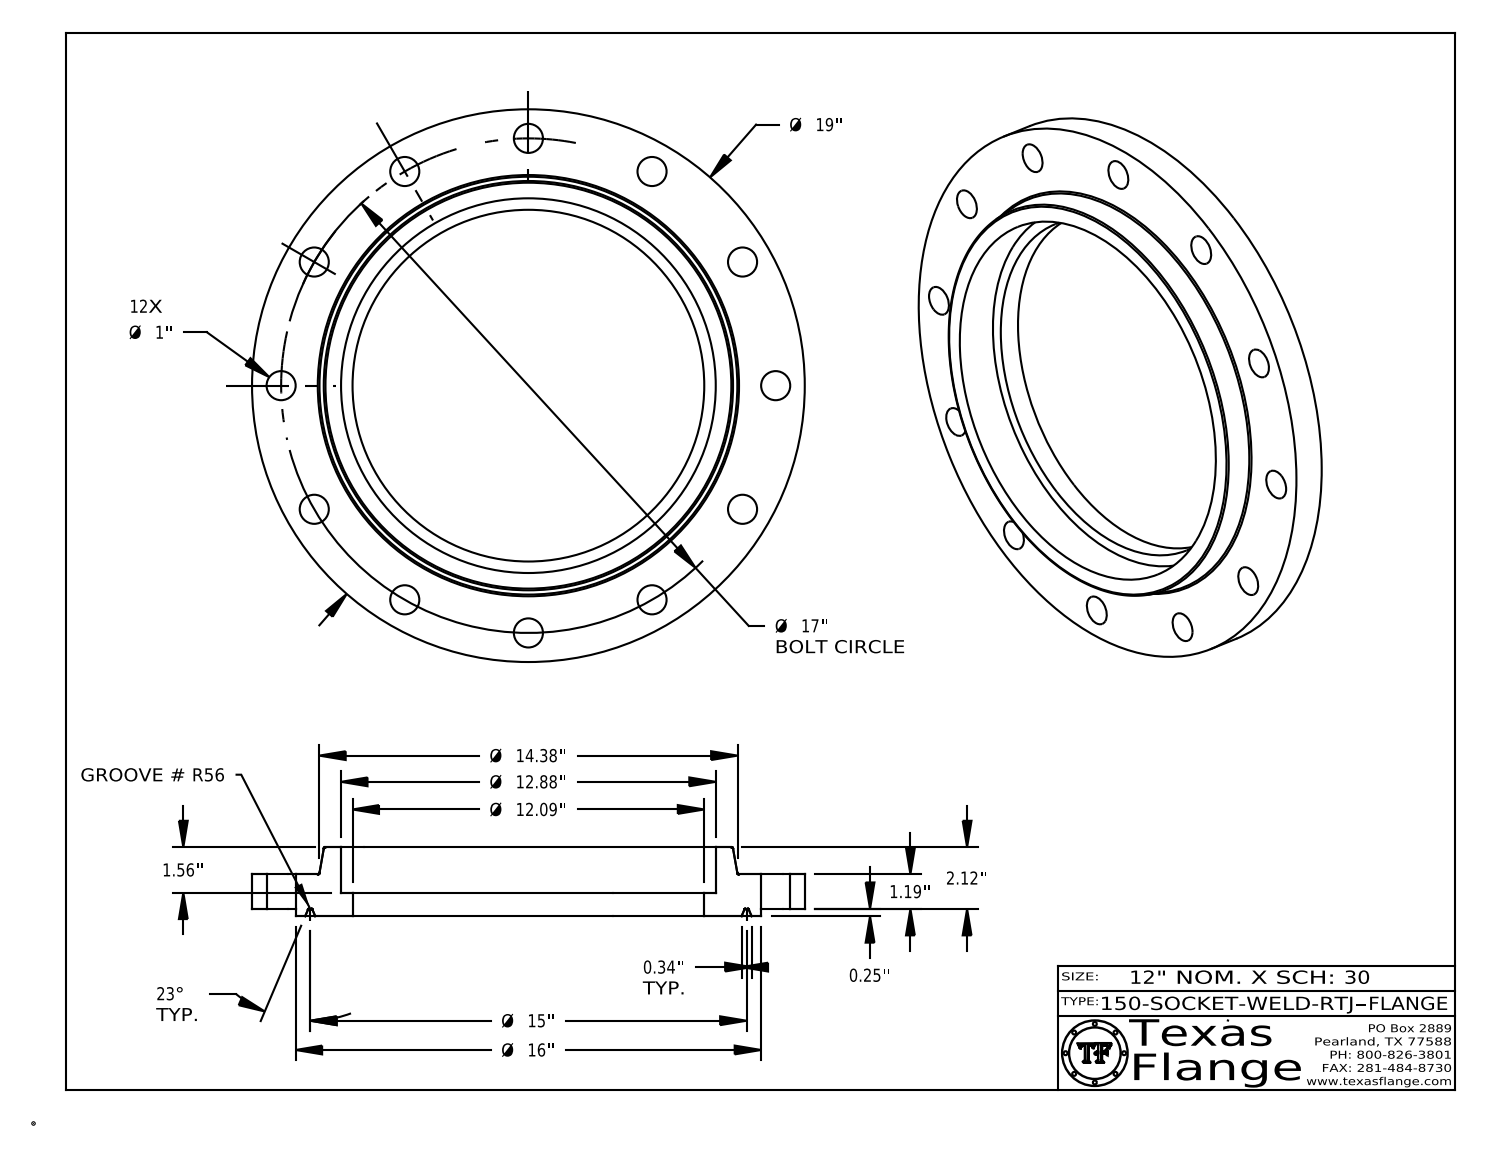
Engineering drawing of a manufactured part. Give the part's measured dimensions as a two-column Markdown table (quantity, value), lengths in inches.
| quantity | value |
| --- | --- |
| part name | 150-SOCKET-WELD-RTJ |
| STEP written by | CATIA V5 STEP AP214 (AUTOMOTIVE_DESIGN) |
| units | inches |
| bodies | 1 solid, 438 faces (372 planar, 52 cylindrical, 14 other) |
| overall size | 19 × 19 × 2.37 |
| volume | 225 in³ |
| surface area | 589.5 in² |
| round holes (diameter × count) | 1 × 12, 0.495 × 1, 12.09 × 1, 12.88 × 1 |
| round bosses / shafts (diameter × count) | 0.03 × 8, 19 × 1, 16 × 1, 0.39 × 1 |
| main face-to-face distances | 1.19, 0.25, 1.44, 2.37, 2.12, 0.93, 0.81, 0.56, 0.63, 1.56 |
| hole center spacings | 8.5, 16.42, 4.4, 12.02, 14.722, 4.4, 12.021, 14.722 |
